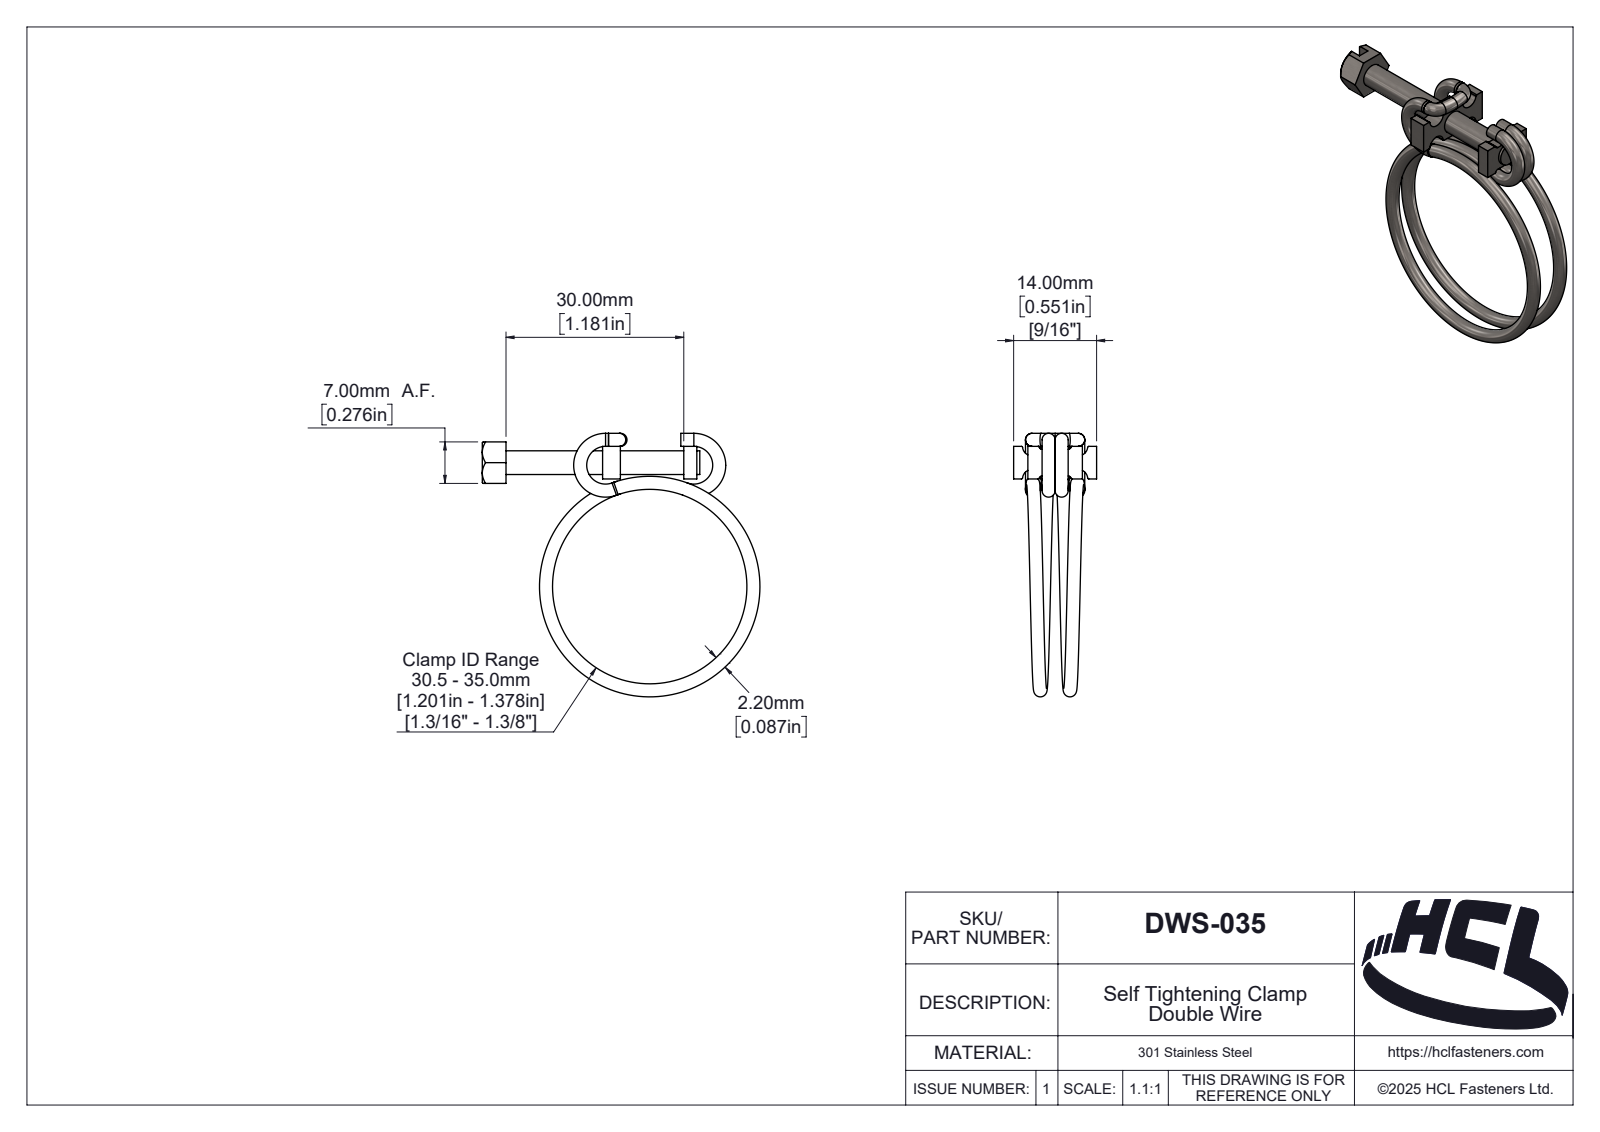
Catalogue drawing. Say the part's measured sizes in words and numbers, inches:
The part is named "DWS-035". Its 3-D file was written by "SolidWorks 2025 (AUTOMOTIVE_DESIGN)". It is 6 solids with 209 faces: 51 planar, 74 cylindrical and 84 other. Overall it measures 1.844 by 1.75 by 0.551 inches. Its volume is 0.121 cubic inches and its surface area 5.072 square inches. Round holes: 1 of diameter 0.157. Round bosses or shafts: 4 of diameter 0.087. Partial cylindrical surfaces (rounded edges, fillets, slot ends): 12 of radius 0.008, 4 of radius 0.02, 4 of radius 0.063, 1 of radius 0.016, 1 of radius 0.02, 1 of radius 0.021, 1 of radius 0.025, 1 of radius 0.036. The main face-to-face distances are 0.079, 0.118, 0.76, 0.276, 0.02, 0.626, 0.508, 0.539, 0.421, 0.087.
